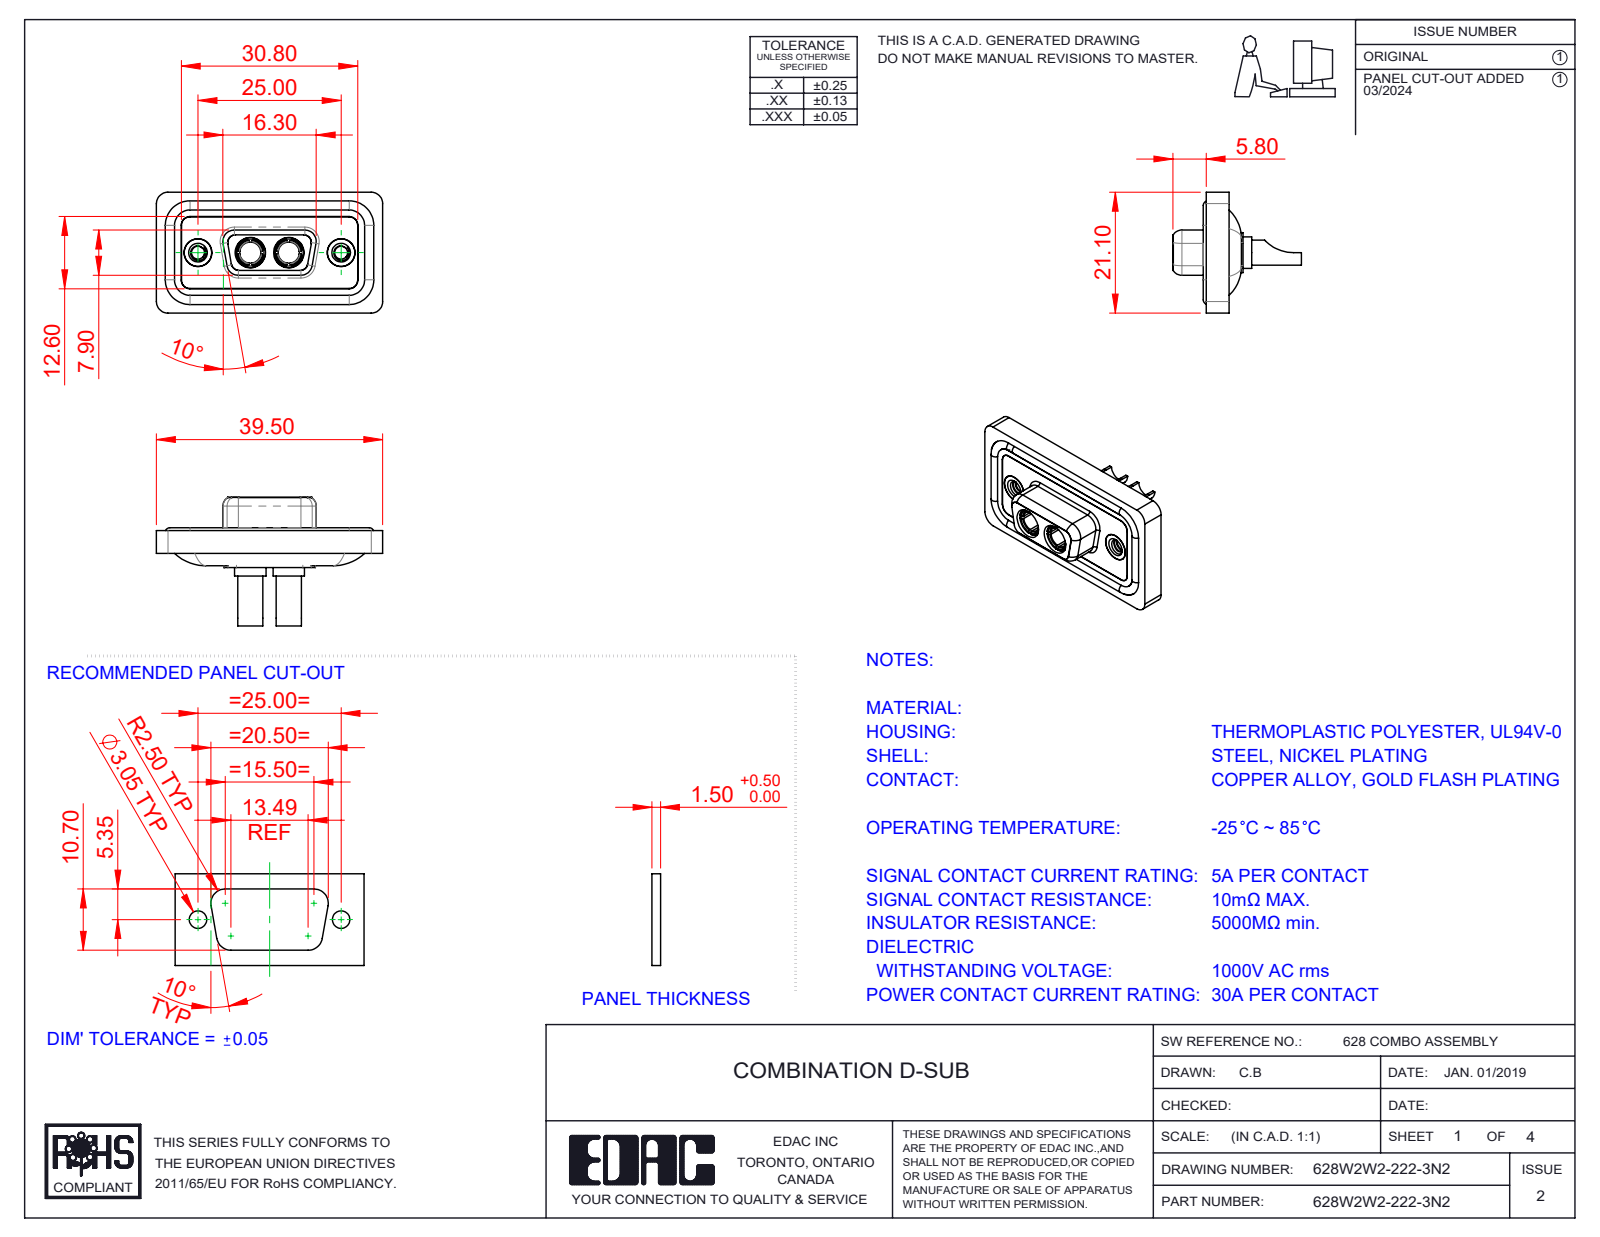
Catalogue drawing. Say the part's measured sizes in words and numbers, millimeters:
The part is named "628Combo Threaded Rivet_2; 628Combo Shell Front_09 Contacts; 628W2W2-222-3N2; 628Combo Housing_2W2 (+3 more)". Its 3-D file was written by "SolidWorks 2023 (CONFIG_CONTROL_DESIGN)". It is 11 solids with 546 faces: 169 planar, 240 cylindrical and 137 other. Overall it measures 39.5 by 22.45 by 21.1 millimeters. Its volume is 4 761 cubic millimeters and its surface area 7 851 square millimeters. Round holes: 4 of diameter 4.85, 2 of diameter 2.26, 2 of diameter 3.5, 2 of diameter 3.7, 2 of diameter 4, 2 of diameter 4.05, 2 of diameter 5, 2 of diameter 5.3. Round bosses or shafts: 4 of diameter 1.6, 2 of diameter 5.5, 2 of diameter 5.2, 2 of diameter 4.96, 2 of diameter 4.95, 2 of diameter 4.8, 2 of diameter 4.75, 2 of diameter 4.4. Partial cylindrical surfaces (rounded edges, fillets, slot ends): 22 of radius 1.5, 18 of radius 2, 8 of radius 1.35, 8 of radius 1.6, 4 of radius 0.25, 4 of radius 0.5, 4 of radius 0.6, 4 of radius 0.65. The main face-to-face distances are 0.4, 1.1, 2.9, 1.8, 0.5, 1.6, 5.65, 7.45, 5.35, 3.1. The hole center spacings are 9.14, 15.86, 6.72, 25.
